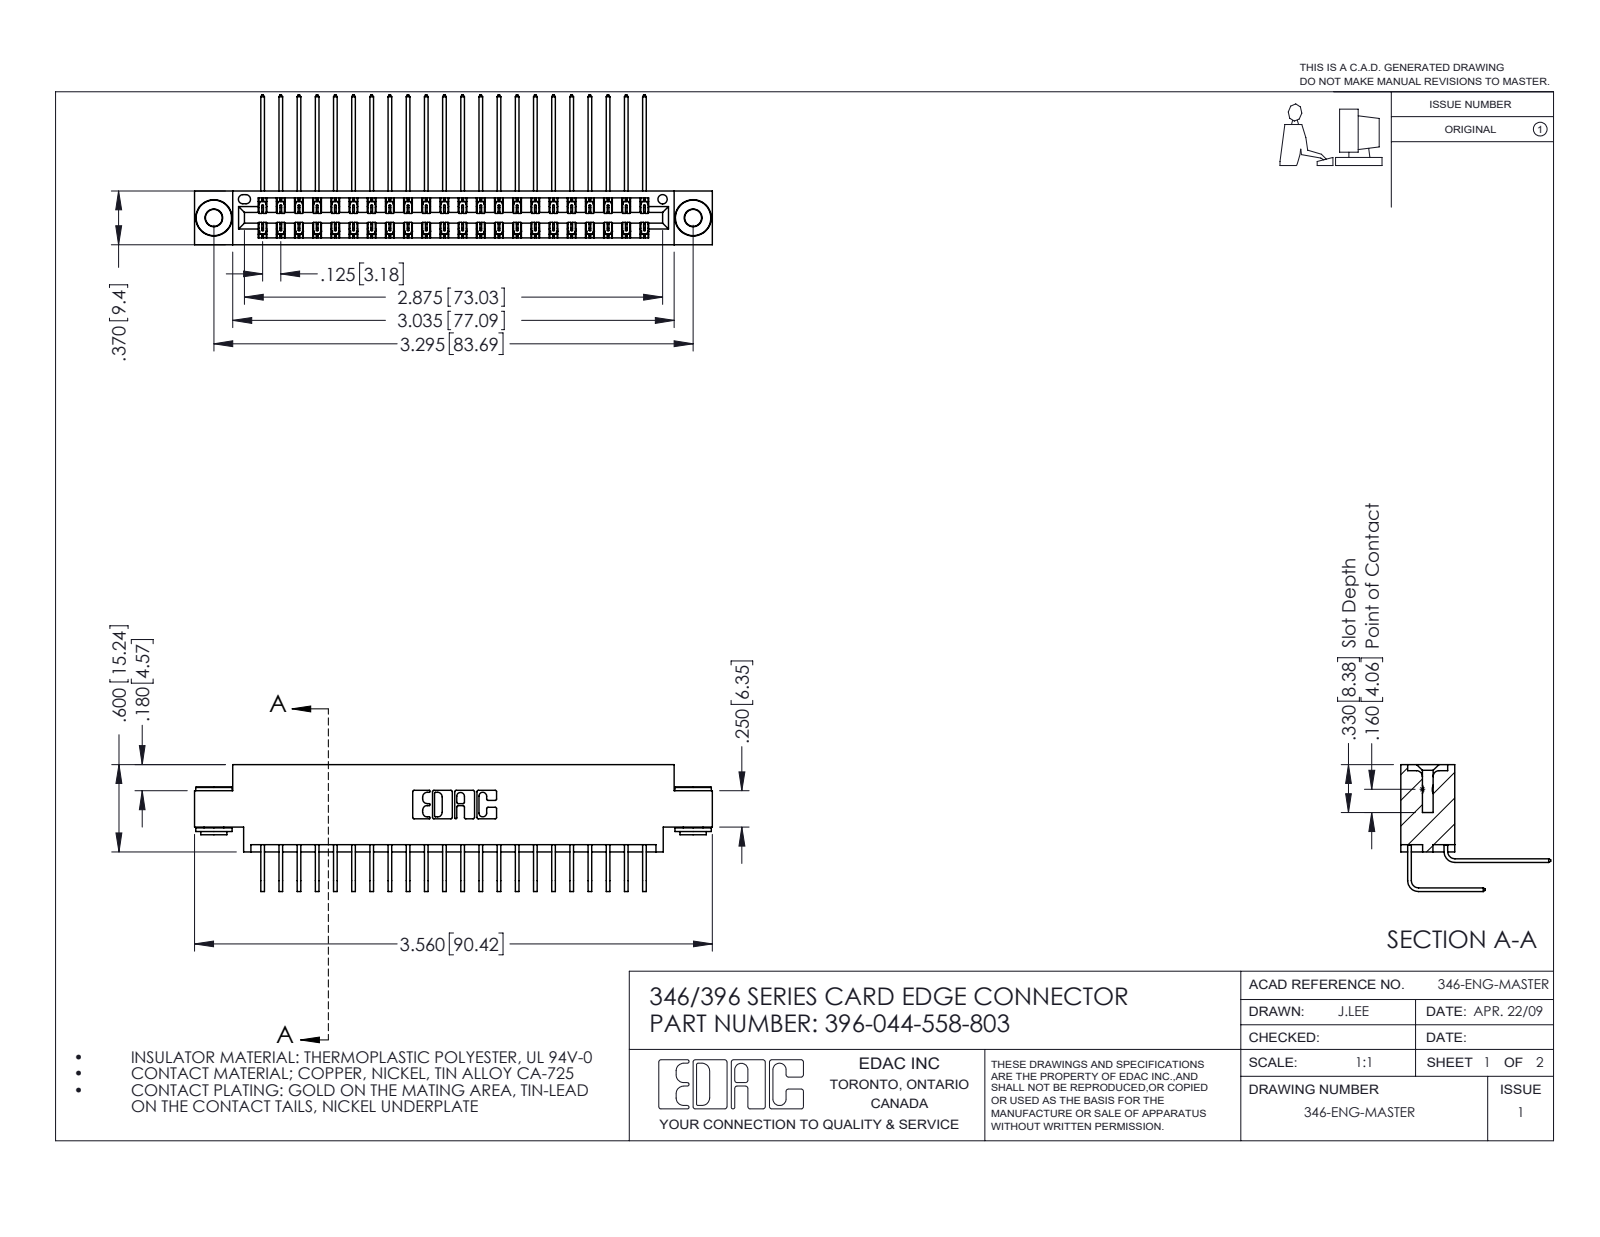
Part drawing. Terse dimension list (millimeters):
name: 345-250-002_345-250-002-102; 396-044-558-803; 345-292-001_558 559 Tail - 1; 345-292-001_558 Tail - 2 (+1 more)
written by: SolidWorks 2016 (CONFIG_CONTROL_DESIGN)
unit: mm
bodies: 47 solids, 2540 faces (1718 planar, 814 cylindrical, 8 other)
size: 90.4 × 26.2 × 22.2
volume: 8 780 mm³; area: 13 370 mm²
holes: 2× ⌀2.9, 2× ⌀4, 1× ⌀1.6
bosses: 2× ⌀6.4, 2× ⌀4.6, 2× ⌀3.5
rounds: 66× R0.2, 22× R0.3, 6× R0.2, 6× R0.8, 3× R0.7, 2× R0.4, 2× R0.6, 2× R0.6
face distances: 8.2, 1.2, 0.6, 9.4, 6.4, 7.6, 1.8, 7, 3.8, 5.6
hole spacings: 6.2, 78.4, 83.7
